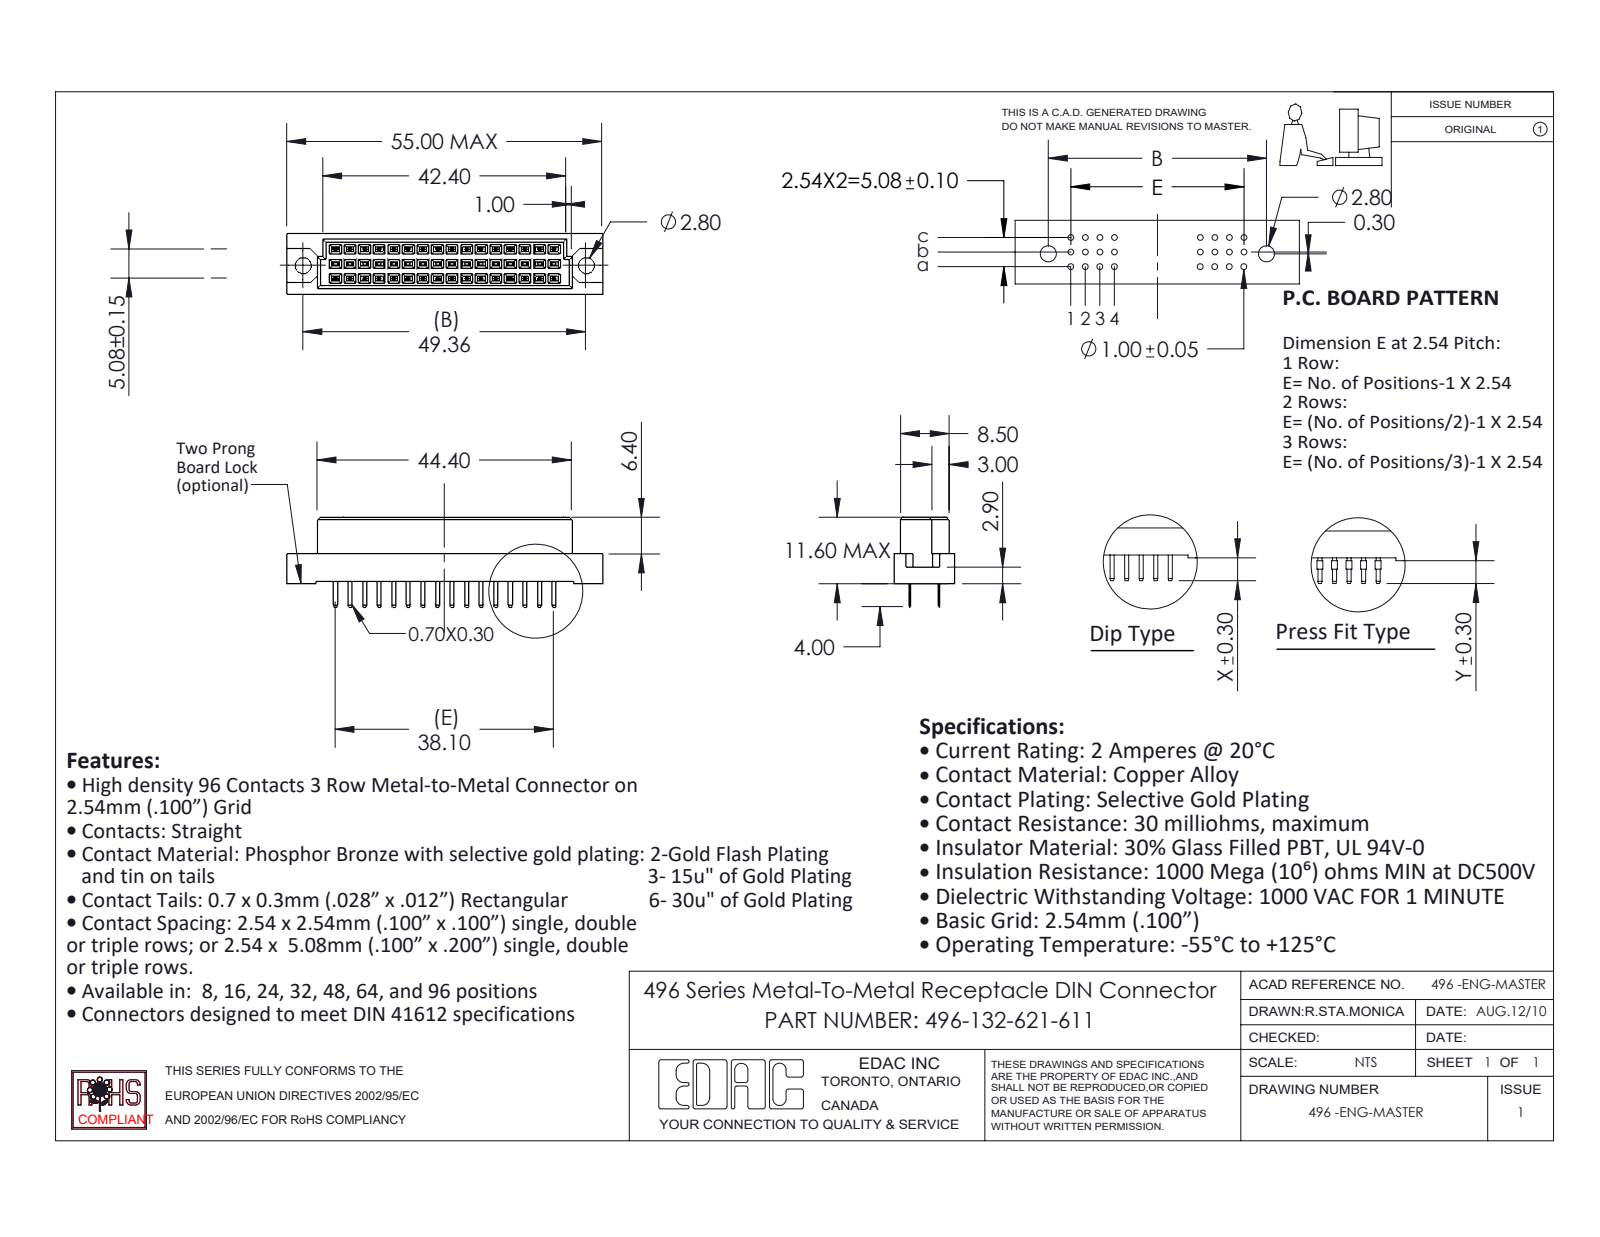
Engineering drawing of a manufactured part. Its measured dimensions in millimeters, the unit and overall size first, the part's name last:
Units: millimetres
Overall size (bounding box): 55 × 15.6 × 10.6
Round holes (diameter × count): ⌀2.8 ×2
Main face-to-face distances: 2.54, 5.08, 1.05, 9.55, 0.81, 0.56, 0.55, 2.61, 2.91, 7.69
Hole centre spacings: 49.36
Volume: 4 644 mm³ · Surface area: 4 748 mm²
Bodies: 33 solids, 986 faces (982 planar, 4 cylindrical, 0 other)
Part name (STEP PRODUCT): 496-132-621-611; 496 Part_48; 496-290_21
STEP written by: SolidWorks 2020 (CONFIG_CONTROL_DESIGN)
